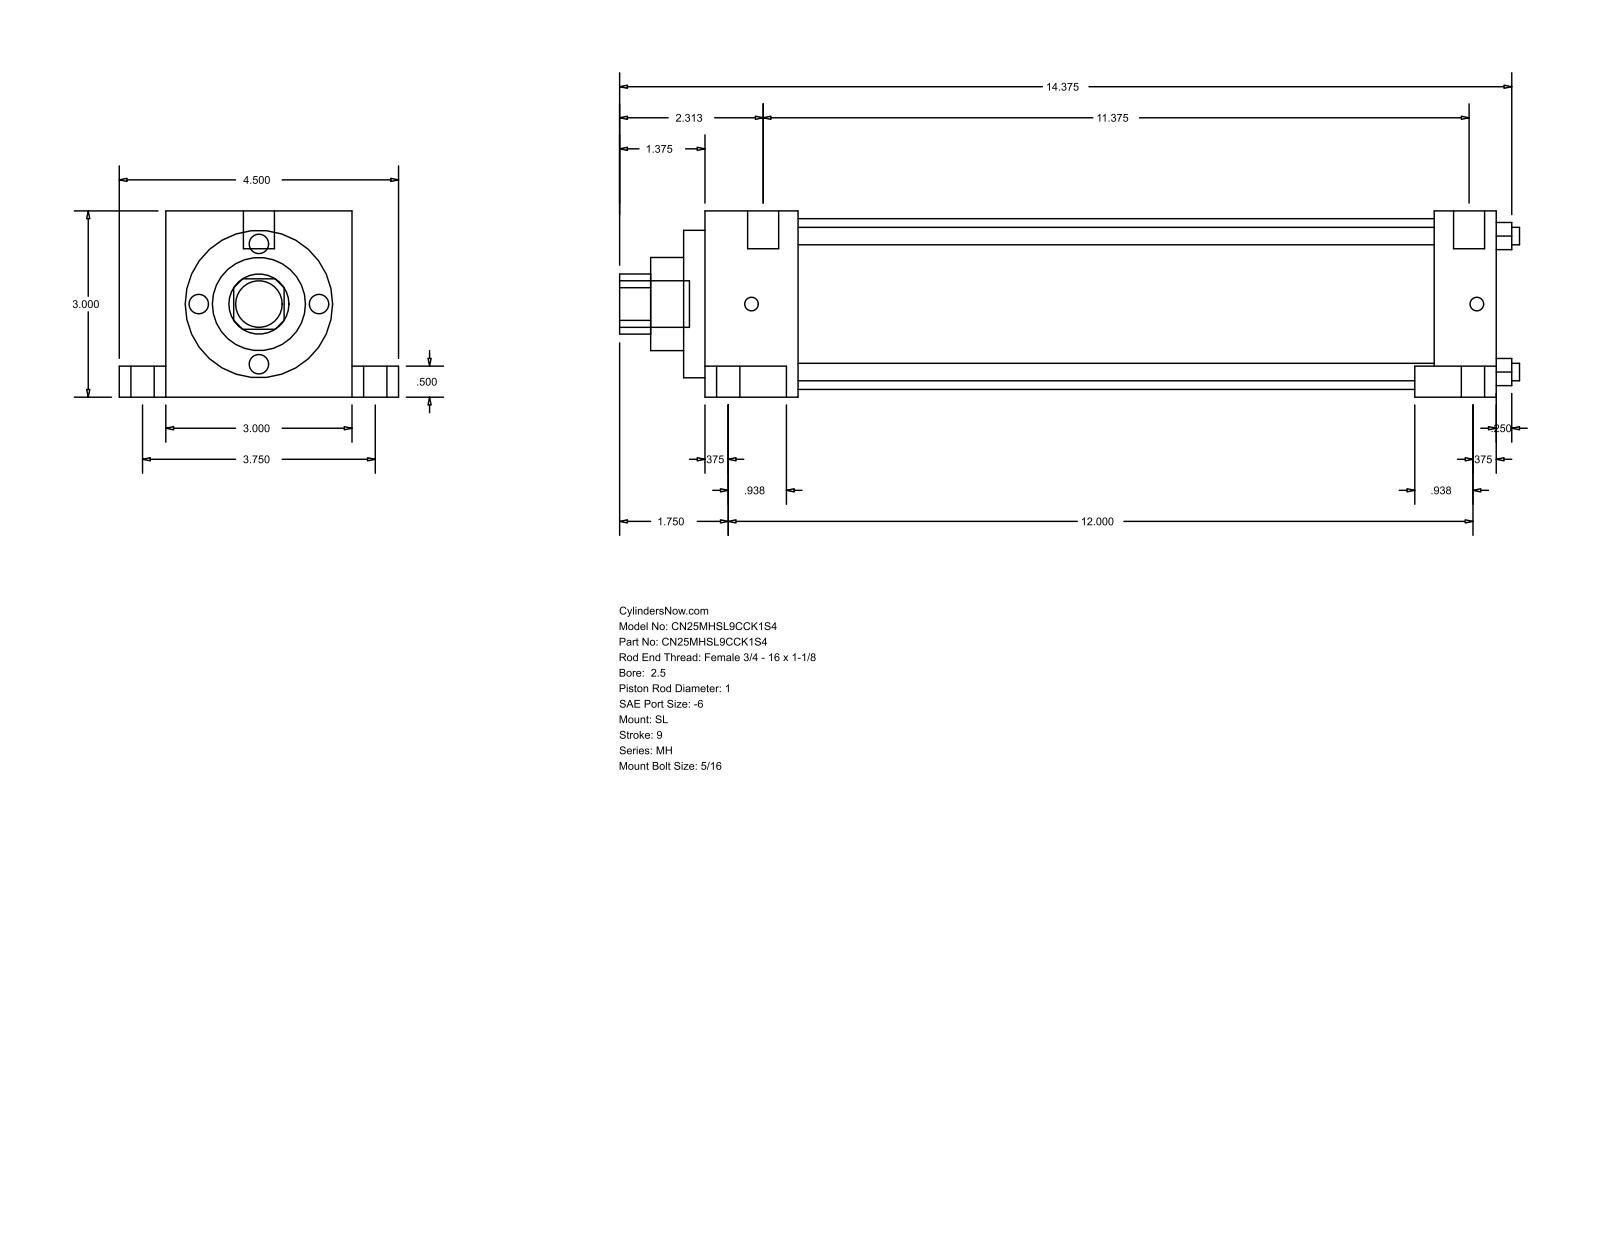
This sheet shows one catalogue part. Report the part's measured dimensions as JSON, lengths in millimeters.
{"part_name": "MH_SL__0250_1", "step_written_by": "GSSL Pune (CONFIG_CONTROL_DESIGN)", "units": "millimeters", "bodies": {"solids": 0, "faces": 86, "planar": 61, "cylindrical": 25, "other": 0}, "overall_size": [368.3, 114.3, 76.2], "round_holes": [[7.14, 4], [25.4, 1], [38.1, 1], [60.33, 1], [69.85, 1]], "round_bosses_or_shafts": [[15.88, 2], [9.53, 2], [5.56, 2], [19.05, 1], [12.7, 1]], "partial_cylinders_radius": [[12.29, 1]], "face_to_face_distances": [76.2, 25.39, 307.19, 332.58, 12.7, 63.5, 19.05, 95.25, 13.49, 320.68], "hole_center_spacings": [39.33, 55.62, 78.66]}
